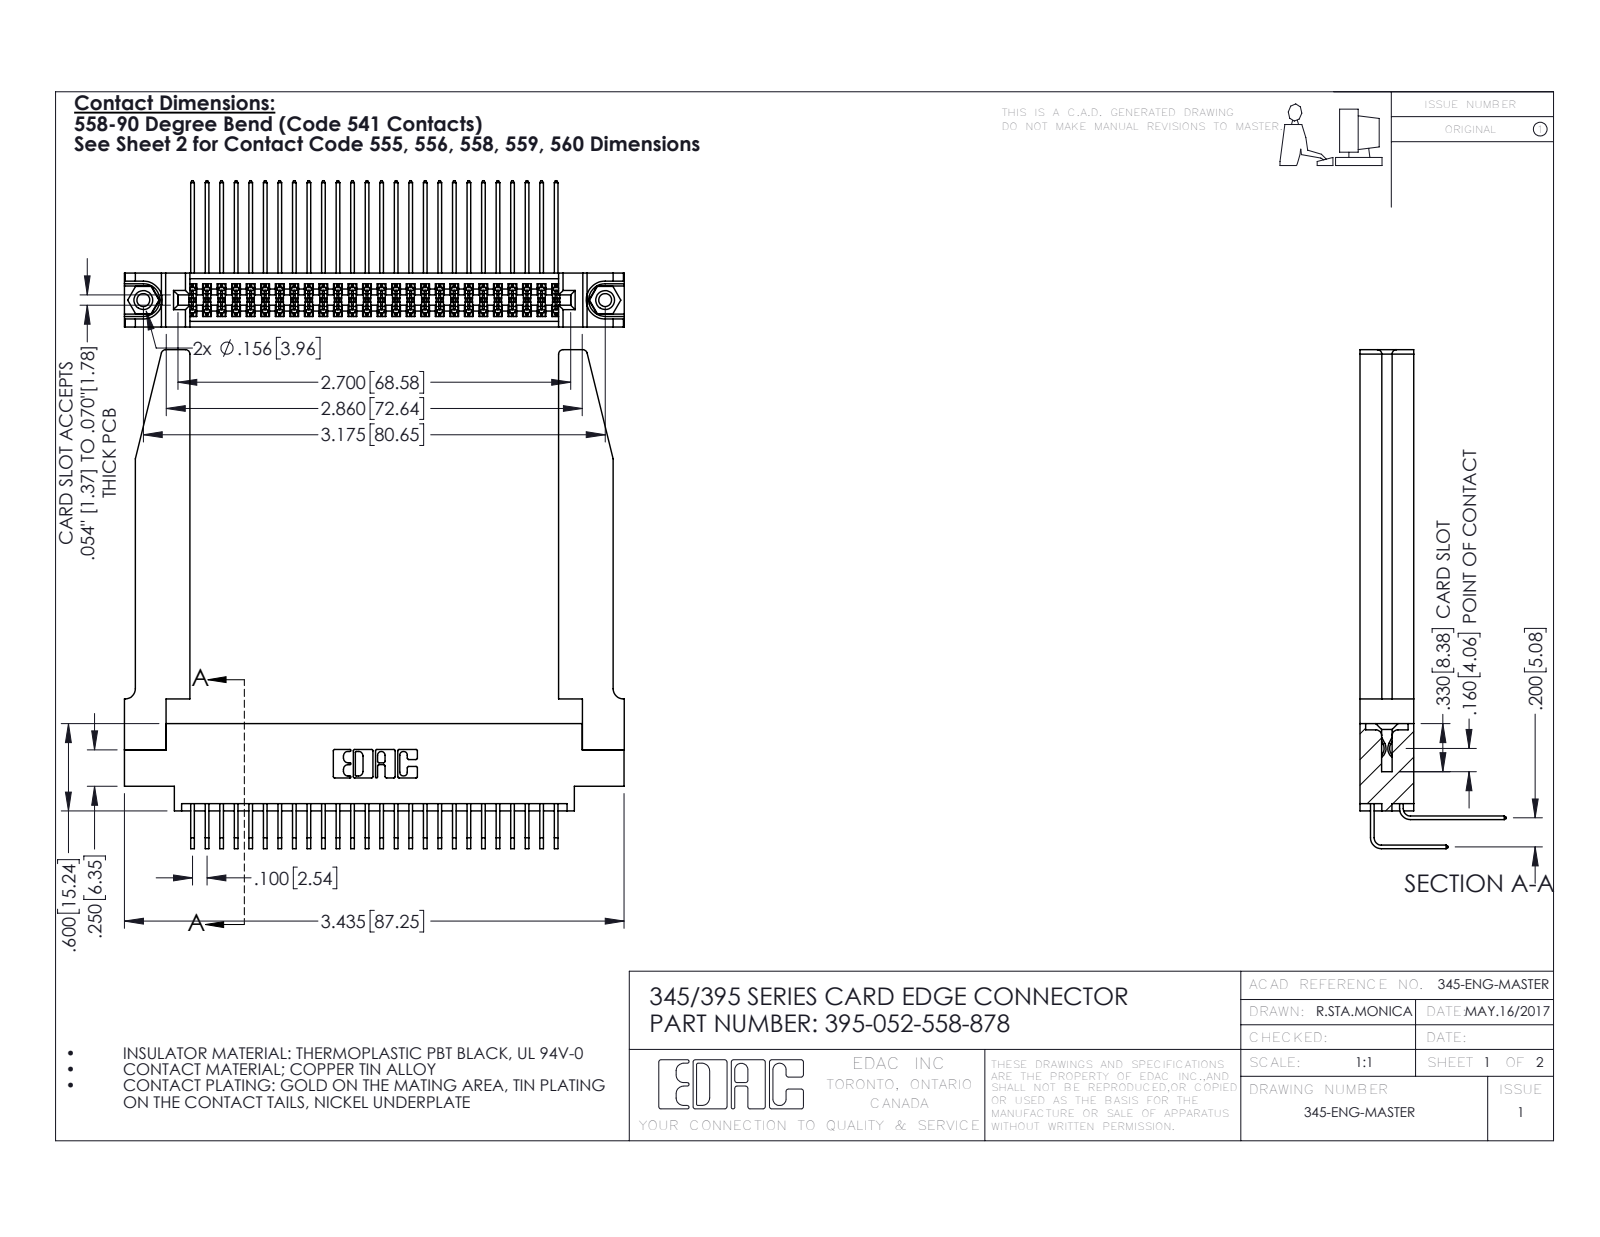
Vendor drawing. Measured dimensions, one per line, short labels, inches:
name: 345-292-001_558 559 Tail - 1; 345-250-001_345-250-001-102; 345-292-001_558 Tail - 2; 345-220-078_345-220-078 (+2 more)
written by: SolidWorks 2016 (CONFIG_CONTROL_DESIGN)
unit: in
bodies: 57 solids, 3068 faces (2046 planar, 970 cylindrical, 52 other)
size: 3.436 × 3.429 × 1.005
volume: 0.994 in³; area: 32.04 in²
holes: 2× ⌀0.089, 2× ⌀0.125, 2× ⌀0.156, 1× ⌀0.064
bosses: 2× ⌀0.155
rounds: 79× R0.006, 22× R0.01, 8× R0.03, 6× R0.007, 6× R0.031, 3× R0.026, 2× R0.014, 2× R0.019
face distances: 0.37, 0.072, 0.298, 0.2, 0.098, 0.272, 0.025, 0.225, 0.148, 0.15
hole spacings: 0.27, 2.94, 3.175
